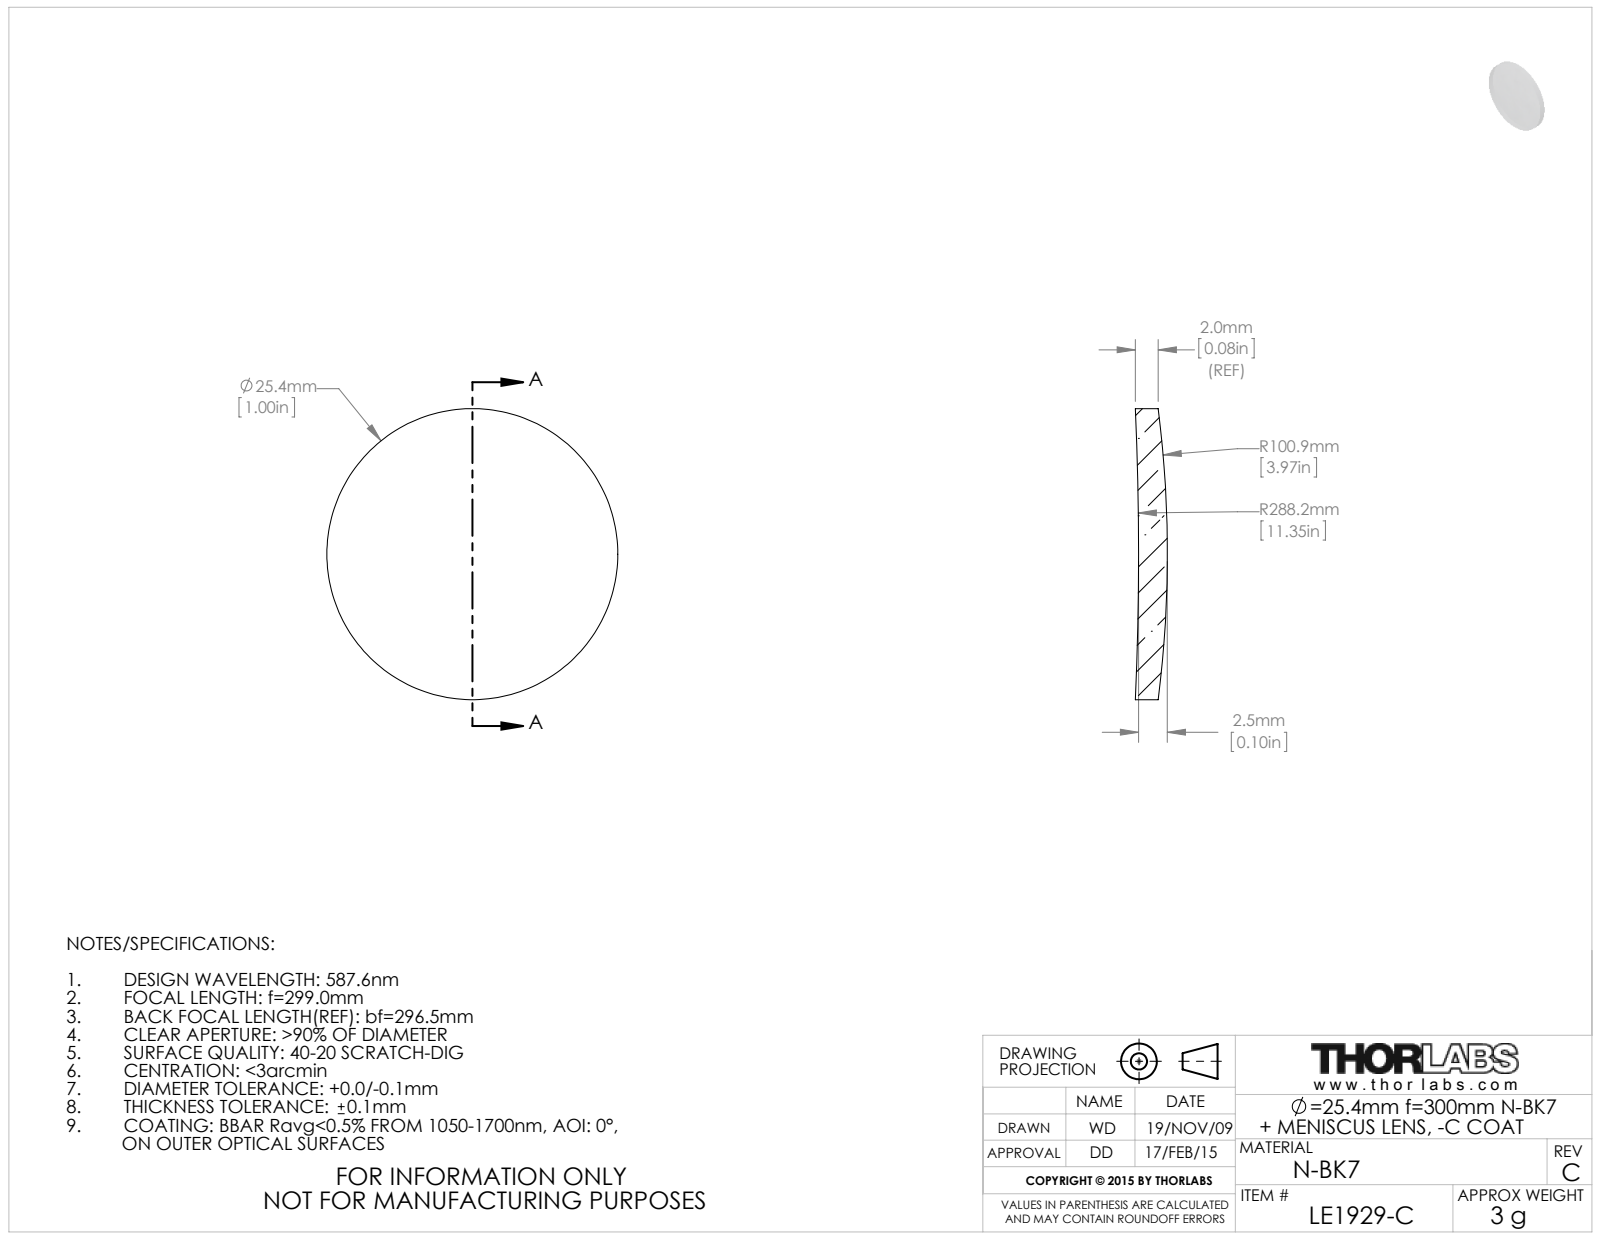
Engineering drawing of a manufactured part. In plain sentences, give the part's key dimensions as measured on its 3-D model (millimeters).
The part is named "4855-E0W". Its 3-D file was written by "SolidWorks 2009 (AUTOMOTIVE_DESIGN)". It is 1 solid with 6 faces: 0 planar, 2 cylindrical and 4 other. Overall it measures 25.4 by 25.4 by 2.8 millimeters. Its volume is 1 145 cubic millimeters and its surface area 1 175 square millimeters. Round bosses or shafts: 1 of diameter 25.4.
